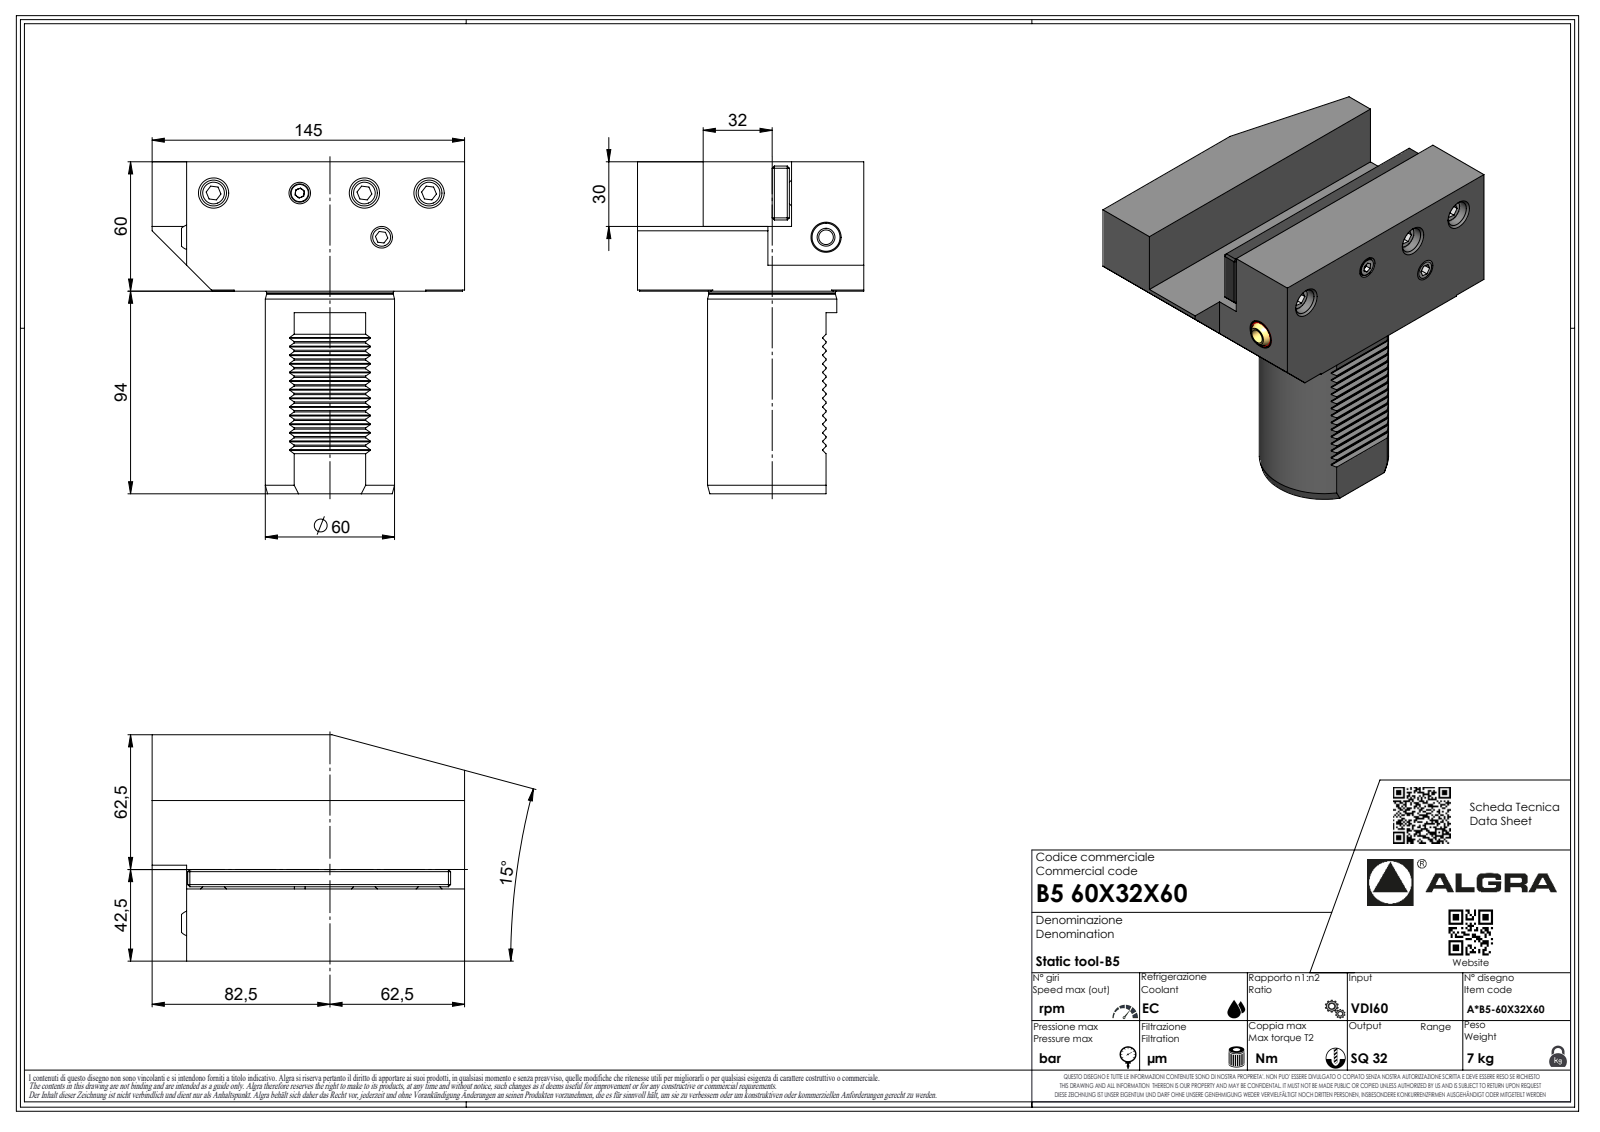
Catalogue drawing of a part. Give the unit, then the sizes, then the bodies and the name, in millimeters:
Units: millimetres
Overall size (bounding box): 154 × 145 × 105
Round holes (diameter × count): ⌀2.1 ×1
Round bosses / shafts (diameter × count): ⌀60 ×1, ⌀58.7 ×1, ⌀6.37 ×1, ⌀1.7 ×1
Partial cylindrical surfaces — rounded edges, fillets, slot ends (radius × count): R0.3 ×14, R0.33 ×7, R0.52 ×7, R3.7 ×7, R0.21 ×1, R61.5 ×1
Main face-to-face distances: 30, 60, 105, 30.5, 74.5, 62.5, 32, 42.5, 94, 124
Volume: 920 817 mm³ · Surface area: 81 458 mm²
Bodies: 1 solid, 379 faces (250 planar, 45 cylindrical, 84 other)
Part name (STEP PRODUCT): B560X32X60
STEP written by: SolidWorks 2023 (AUTOMOTIVE_DESIGN)
